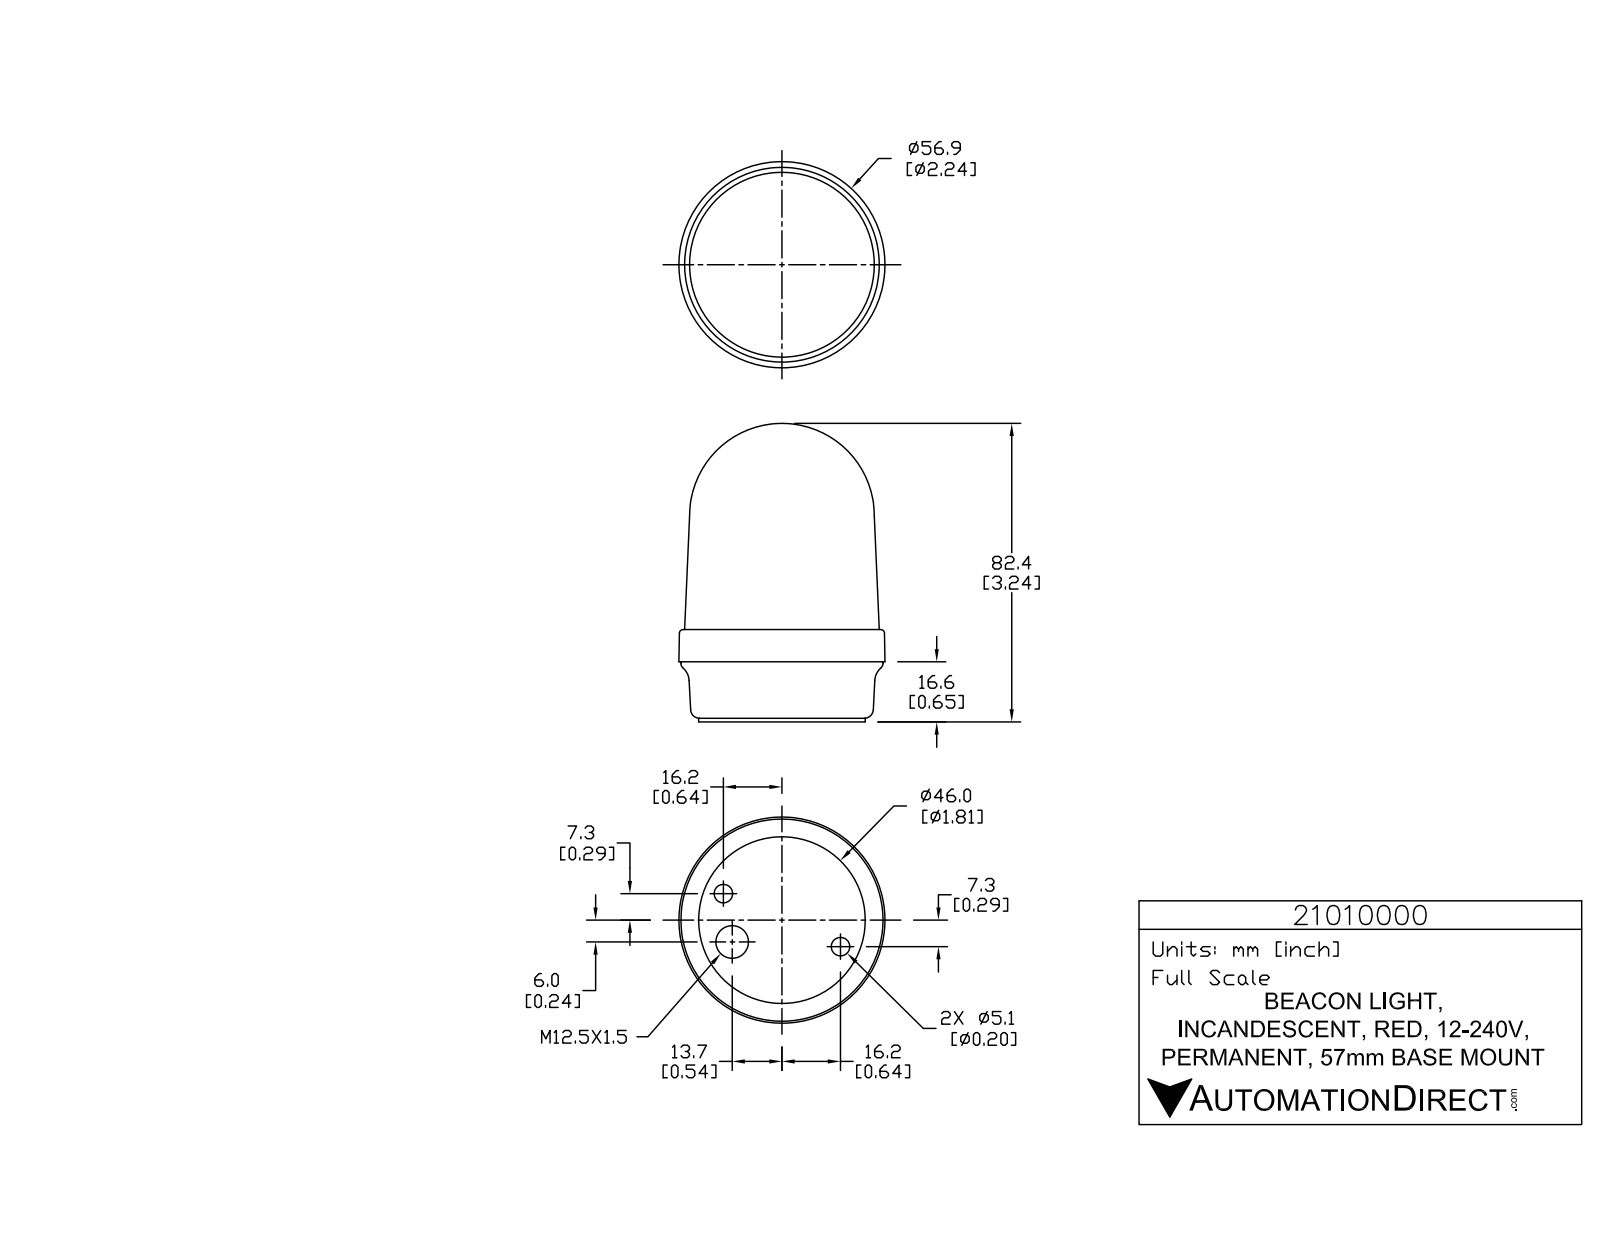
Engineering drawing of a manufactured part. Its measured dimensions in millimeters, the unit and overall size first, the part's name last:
Units: millimetres
Overall size (bounding box): 82.4 × 56.9 × 56.9
Round holes (diameter × count): ⌀1 ×3, ⌀5.1 ×2, ⌀9 ×1
Round bosses / shafts (diameter × count): ⌀5.7 ×3, ⌀1.4 ×3, ⌀55.8 ×1, ⌀46 ×1
Partial cylindrical surfaces — rounded edges, fillets, slot ends (radius × count): R0.2 ×6, R0.2 ×6, R0.2 ×6, R3.3 ×6, R0.1 ×3, R0.1 ×3, R0.2 ×3, R0.2 ×3
Main face-to-face distances: 1, 16.6, 15.6, 25.5, 24.5, 8.9, 10.6, 36.1, 35.1, 19.5
Hole centre spacings: 13.6, 29.9, 35.5
Volume: 159 000 mm³ · Surface area: 16 000 mm²
Bodies: 1 solid, 778 faces (526 planar, 160 cylindrical, 92 other)
Part name (STEP PRODUCT): 21010000
STEP written by: SolidWorks 2015 (AUTOMOTIVE_DESIGN)
